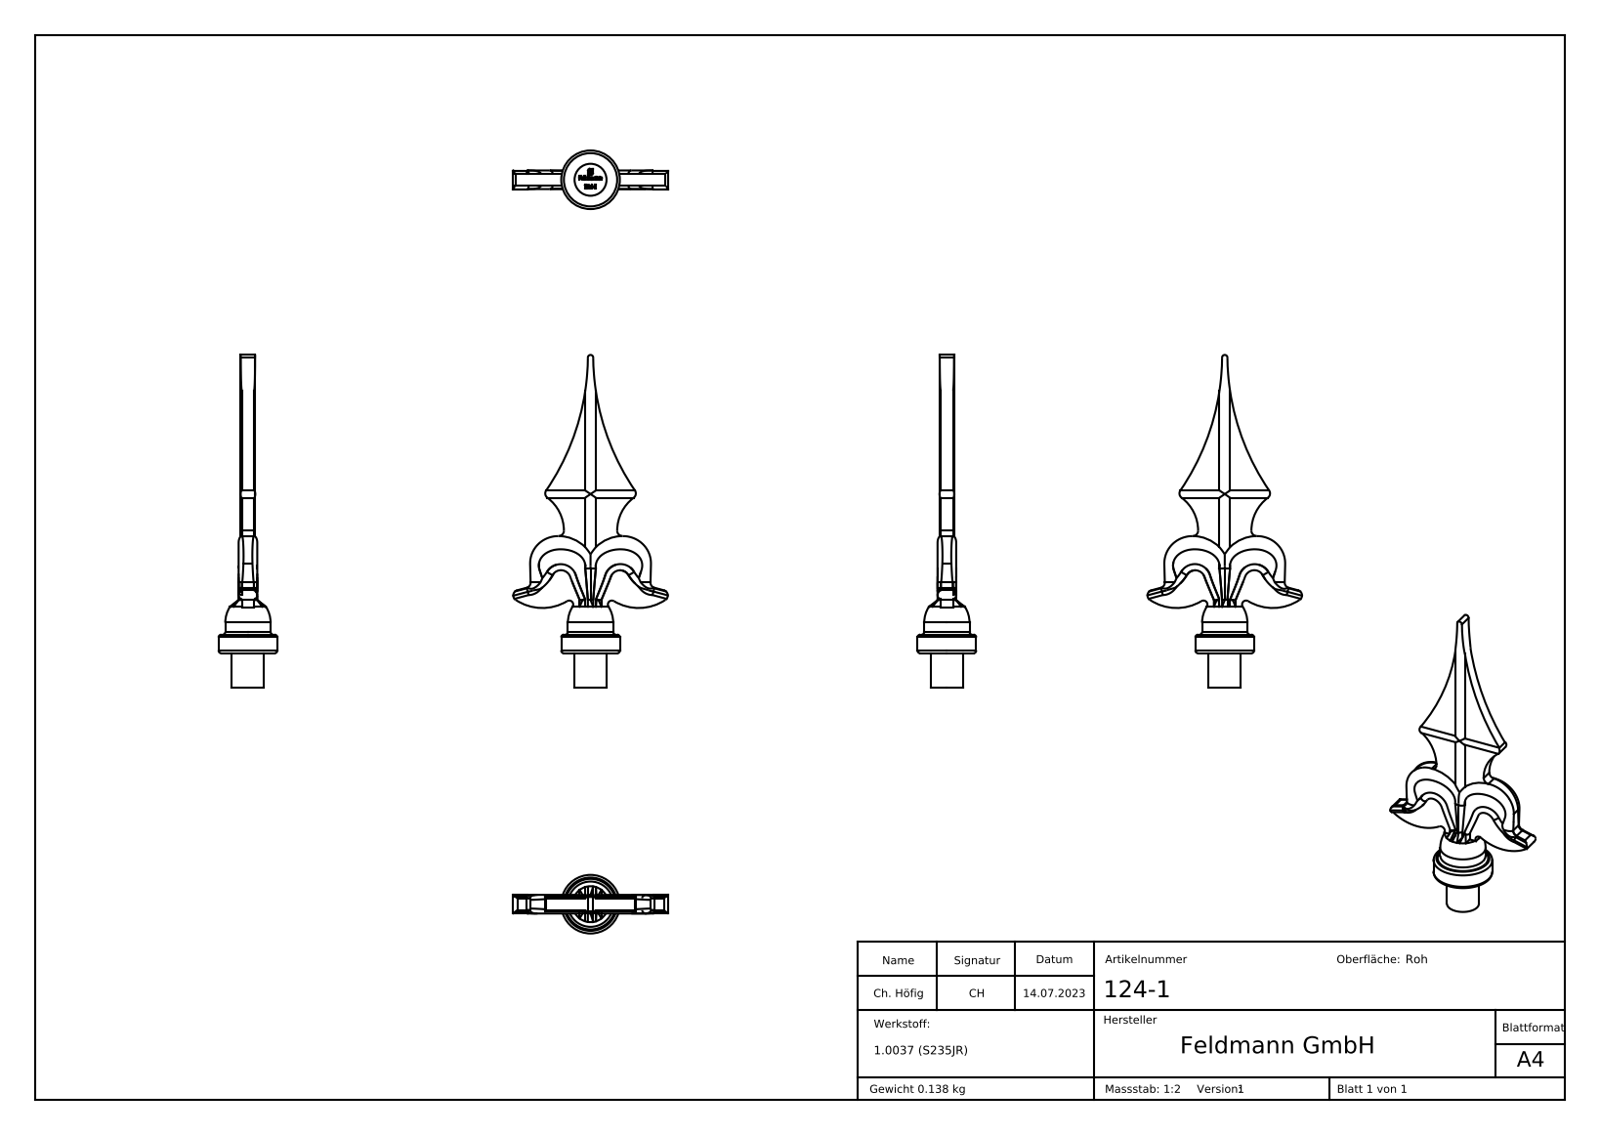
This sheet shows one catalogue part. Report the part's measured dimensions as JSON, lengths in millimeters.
{"part_name": "124-1", "step_written_by": "SolidWorks 2018 (CONFIG_CONTROL_DESIGN)", "units": "millimeters", "bodies": {"solids": 1, "faces": 338, "planar": 164, "cylindrical": 22, "other": 152}, "overall_size": [125, 58, 22], "volume_mm3": 17709, "surface_area_mm2": 9155, "round_bosses_or_shafts": [[22, 1], [17, 1], [12, 1]], "partial_cylinders_radius": [[2, 8], [1.5, 2], [10.5, 2], [15.5, 2], [18, 2], [90, 2], [1, 1]], "face_to_face_distances": [4.5, 13, 2.52, 1.02, 2.25, 30.49, 17.49, 1.29, 3.66, 1.35]}
